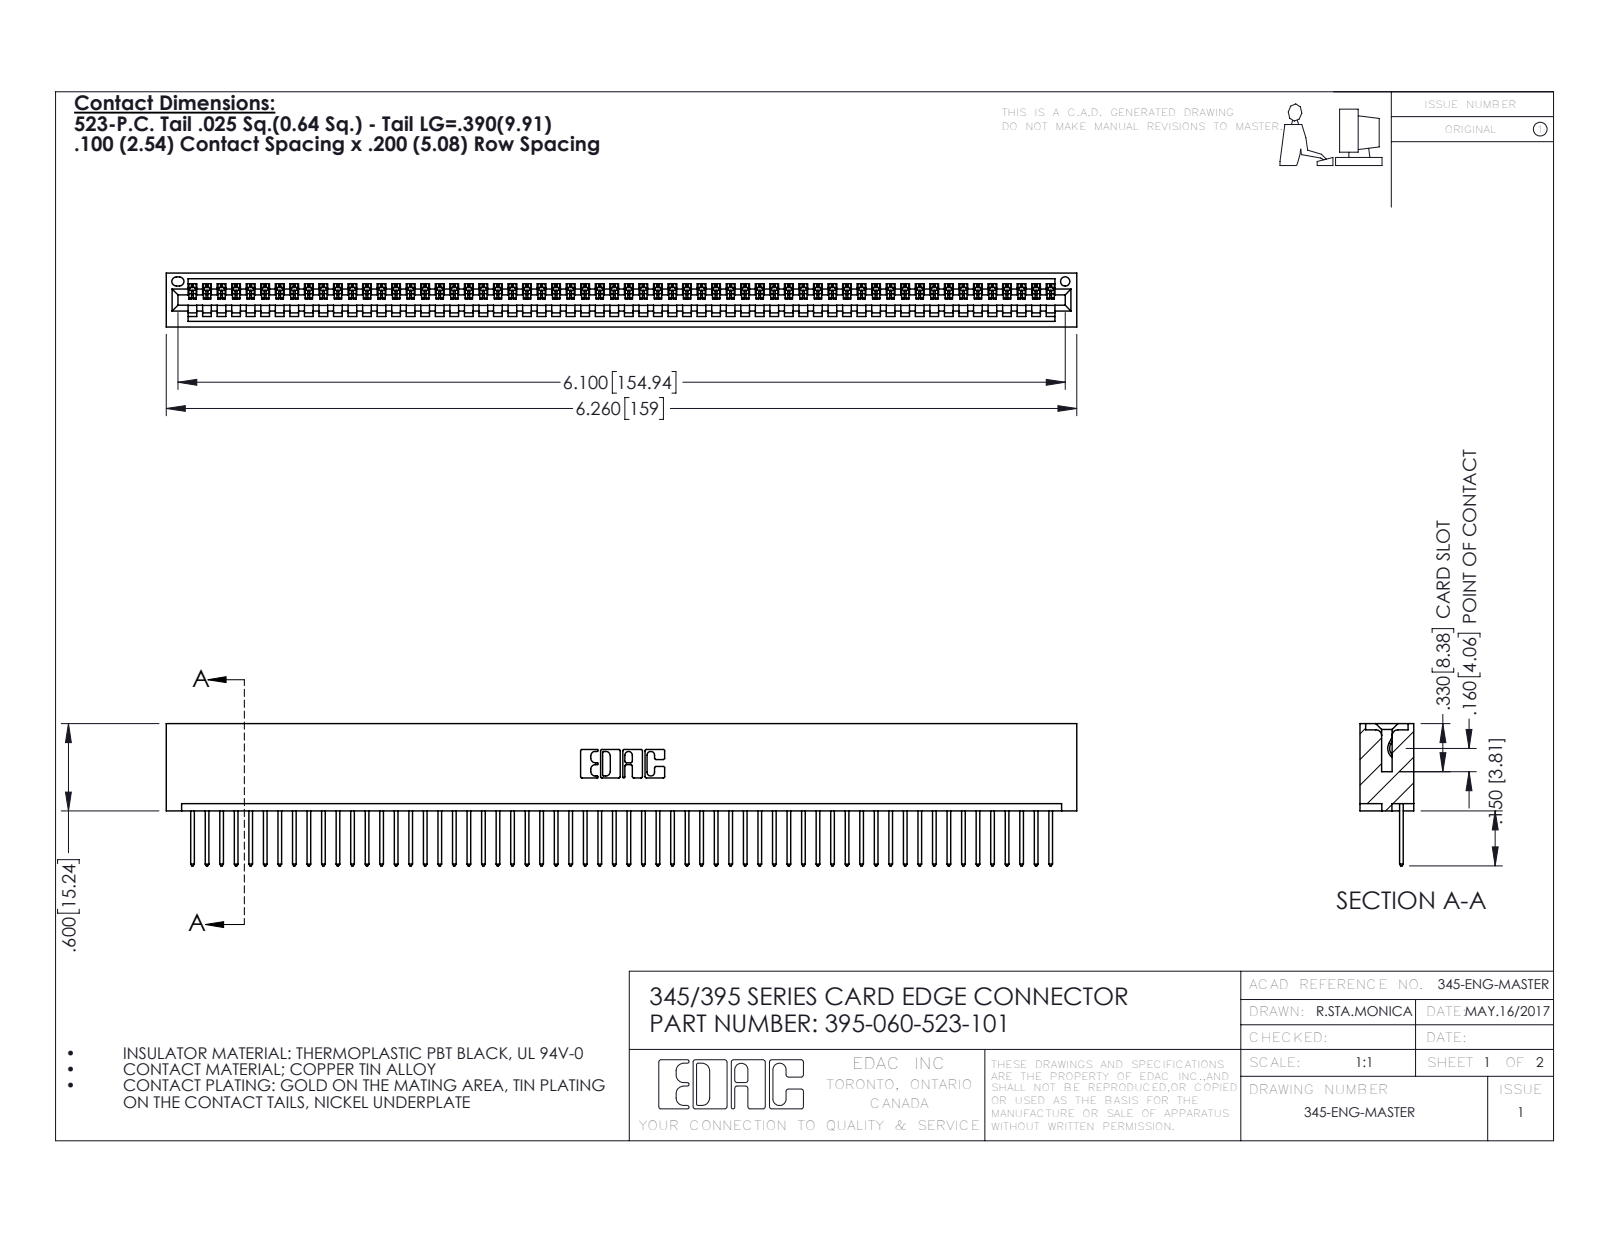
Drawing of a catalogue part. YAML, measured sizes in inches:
part_name: "345 Part_No Mounting Lugs; 345-292-001_345-293-123; 395-060-523-101"
step_written_by: "SolidWorks 2016 (CONFIG_CONTROL_DESIGN)"
units: inches
bodies: {solids: 61, faces: 3598, planar: 2476, cylindrical: 1122, other: 0}
overall_size: [6.26, 0.977, 0.37]
volume: 0.965
surface_area: 33.34
round_holes:
  - {diameter: 0.064, count: 1}
partial_cylinders:
  - {radius: 0.006, count: 120}
  - {radius: 0.01, count: 120}
  - {radius: 0.01, count: 22}
  - {radius: 0.007, count: 6}
  - {radius: 0.031, count: 6}
  - {radius: 0.026, count: 3}
  - {radius: 0.031, count: 2}
  - {radius: 0.04, count: 2}
face_to_face_distances: [0.298, 0.072, 0.37, 0.2, 0.098, 0.272, 0.025, 0.225, 0.149, 0.072]
